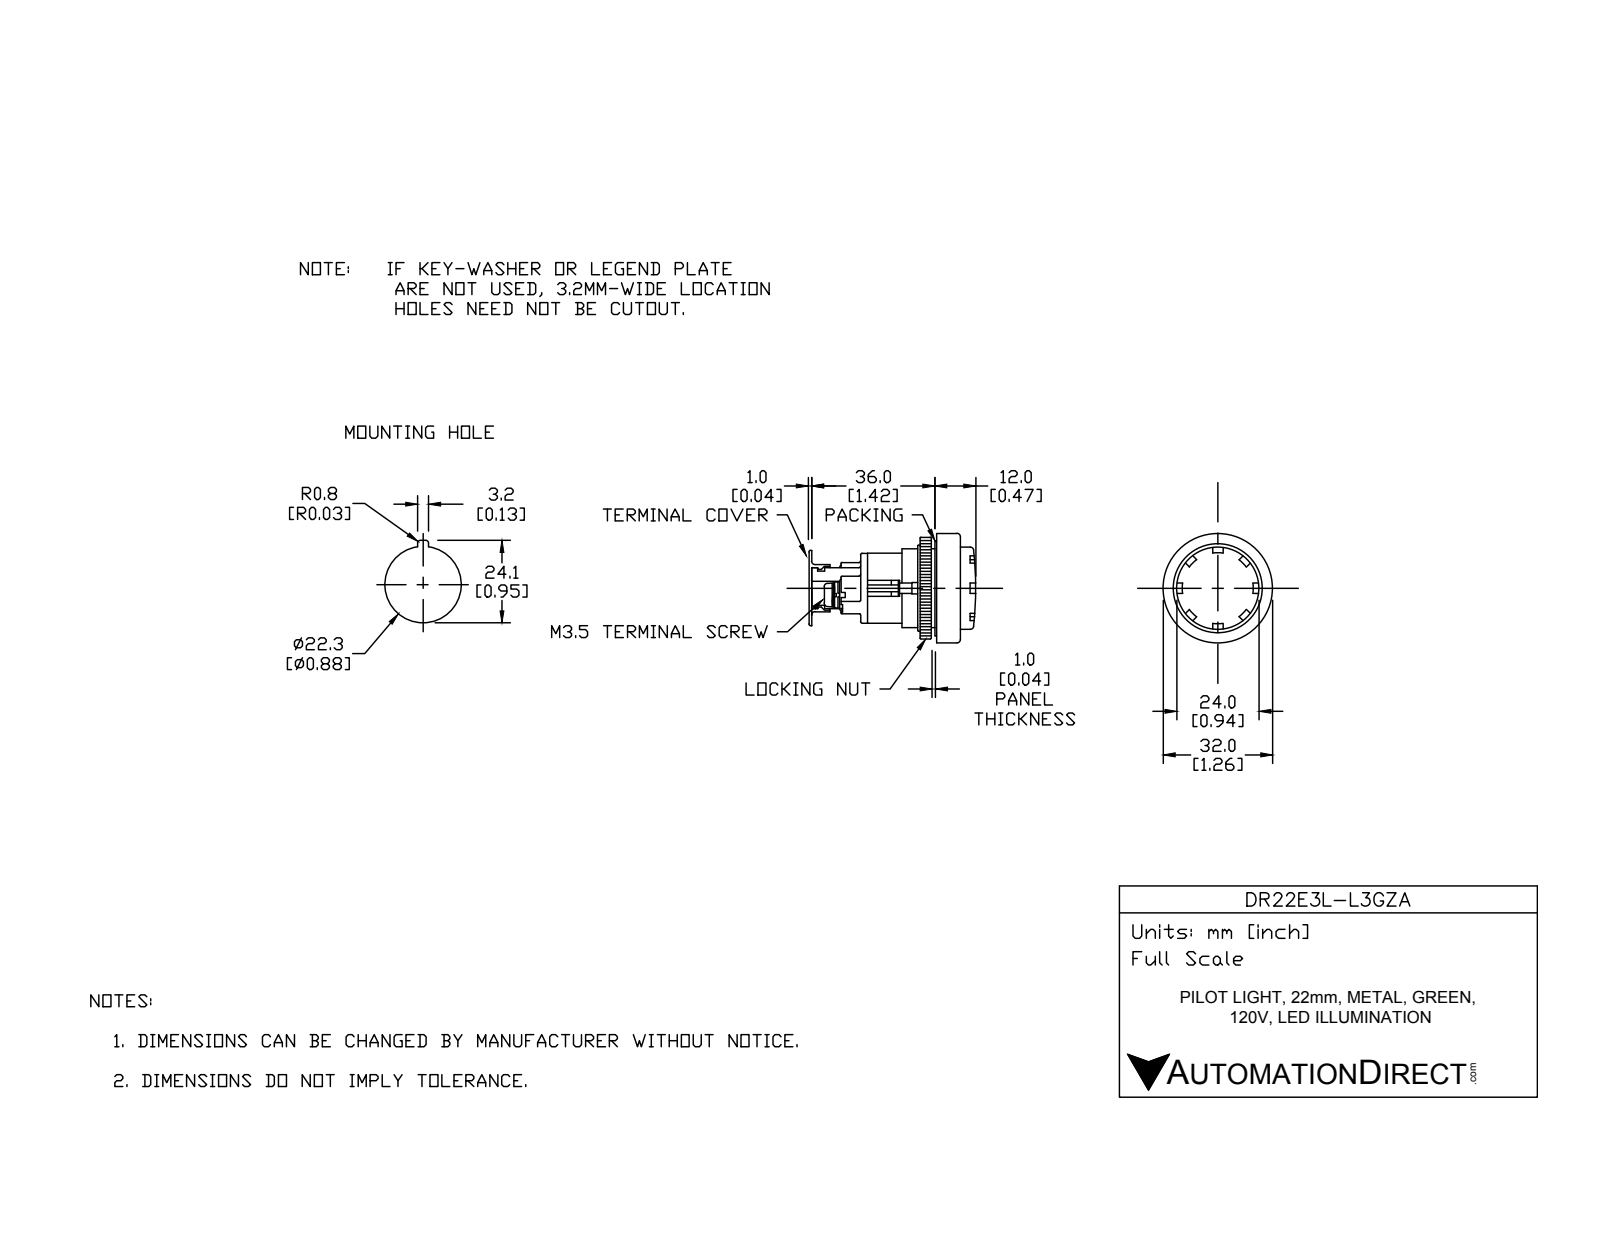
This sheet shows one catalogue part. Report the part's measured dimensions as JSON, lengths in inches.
{"part_name": "DR22E3L-L3GZA", "step_written_by": "SolidWorks 2017 (AUTOMOTIVE_DESIGN)", "units": "inches", "bodies": {"solids": 12, "faces": 232, "planar": 165, "cylindrical": 51, "other": 16}, "overall_size": [2.913, 1.26, 1.26], "volume_in3": 2.435, "surface_area_in2": 28.15, "round_holes": [[0.866, 1], [0.886, 1], [0.984, 1], [1.181, 1]], "round_bosses_or_shafts": [[0.217, 2], [1.26, 1], [1.169, 1], [1.161, 1], [1.063, 1], [0.858, 1]], "partial_cylinders_radius": [[0.02, 14], [0.128, 4], [0.039, 1], [0.197, 1]], "face_to_face_distances": [0.748, 1.181, 1.055, 0.039, 0.157, 0.236, 0.819, 0.433, 1.28, 0.063]}
